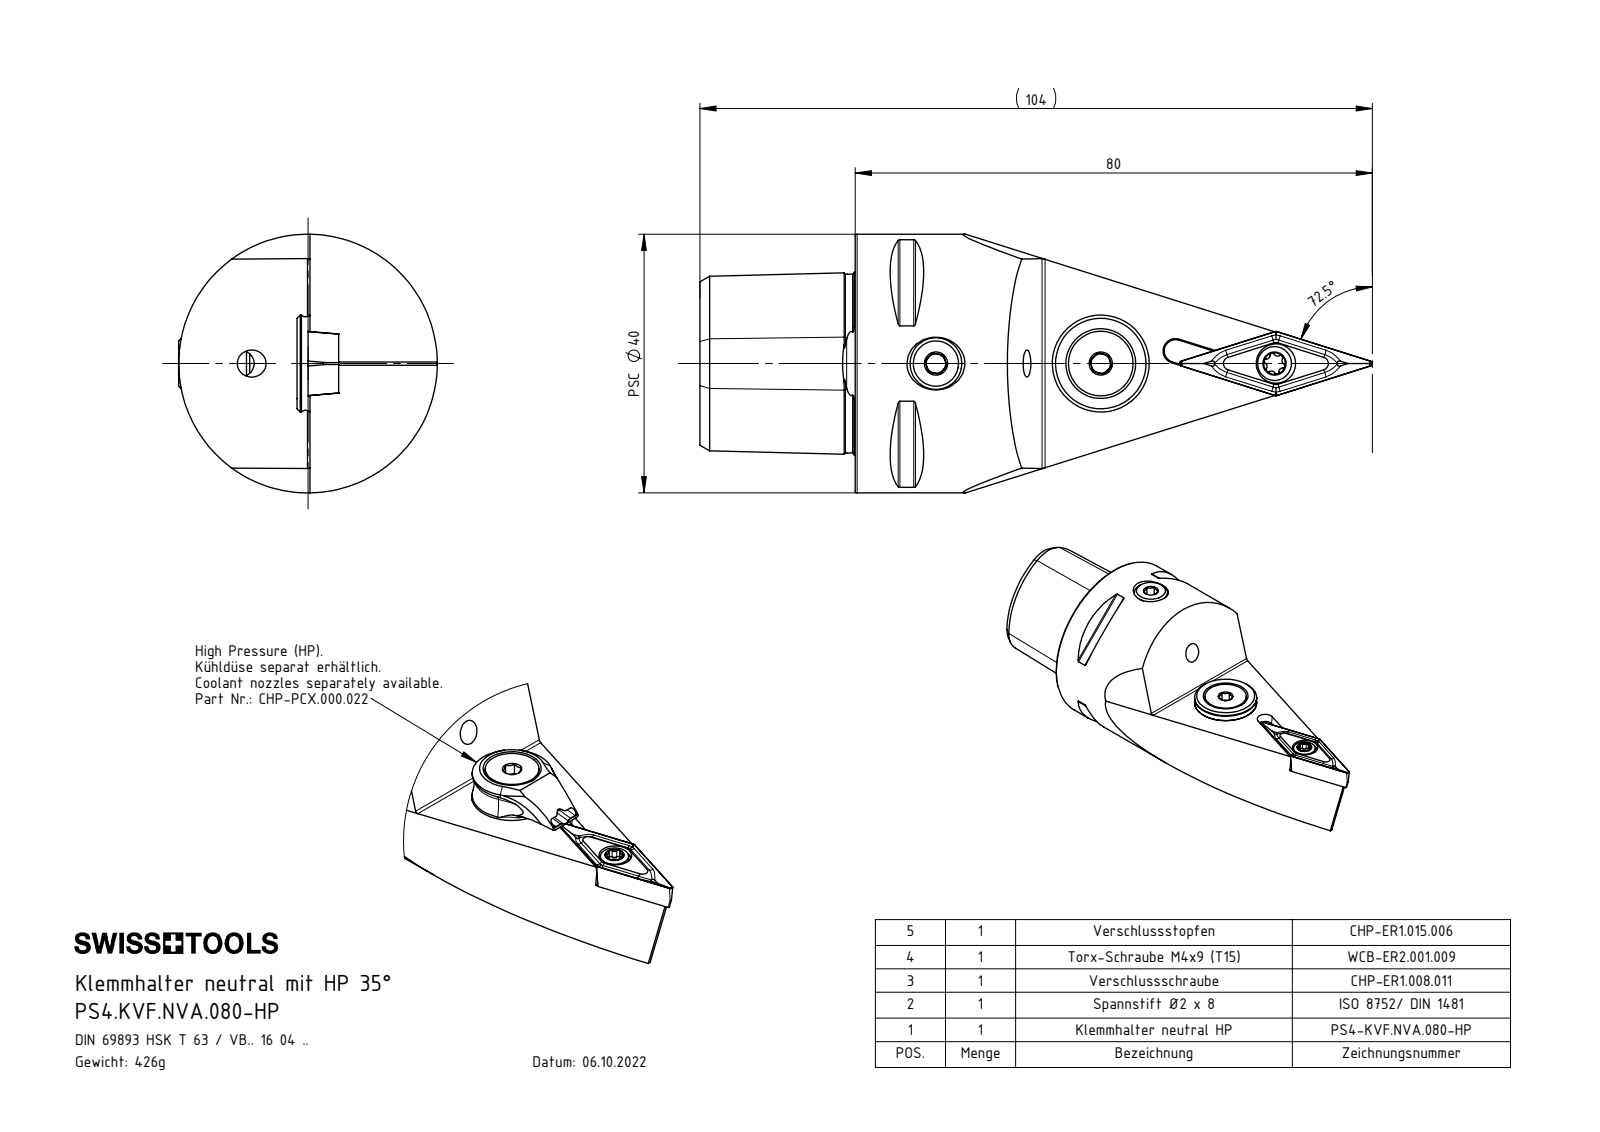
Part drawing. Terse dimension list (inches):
name: CHP-ER1.008.011_A; DIN 3771 - 13x1; CHP-PCX.000.022_B; PS4.KVF.NVA.080-HP (+7 more)
written by: SolidWorks 2022 (AUTOMOTIVE_DESIGN)
unit: in
bodies: 9 solids, 487 faces (103 planar, 130 cylindrical, 254 other)
size: 4.094 × 1.575 × 1.575
volume: 3.291 in³; area: 26.79 in²
holes: 2× ⌀0.13, 2× ⌀0.165, 1× ⌀0.047, 1× ⌀0.079, 1× ⌀0.118, 1× ⌀0.173, 1× ⌀0.181, 1× ⌀0.197, 1× ⌀0.209, 1× ⌀0.24, 1× ⌀0.276, 1× ⌀0.394
bosses: 1× ⌀1.575, 1× ⌀0.585, 1× ⌀0.528, 1× ⌀0.394, 1× ⌀0.315, 1× ⌀0.217, 1× ⌀0.207, 1× ⌀0.197
rounds: 9× R0.012, 7× R0.039, 6× R0.013, 6× R0.023, 3× R0.02, 3× R0.236, 2× R0.006, 2× R0.043
face distances: 0.176, 0.368, 0.945, 0.177, 0.611, 0.059, 0.118, 0.057, 1.39, 0.354
hole spacings: 0.177, 0.236, 0.787, 0.925, 0.927, 0.932, 0.935, 1.024
